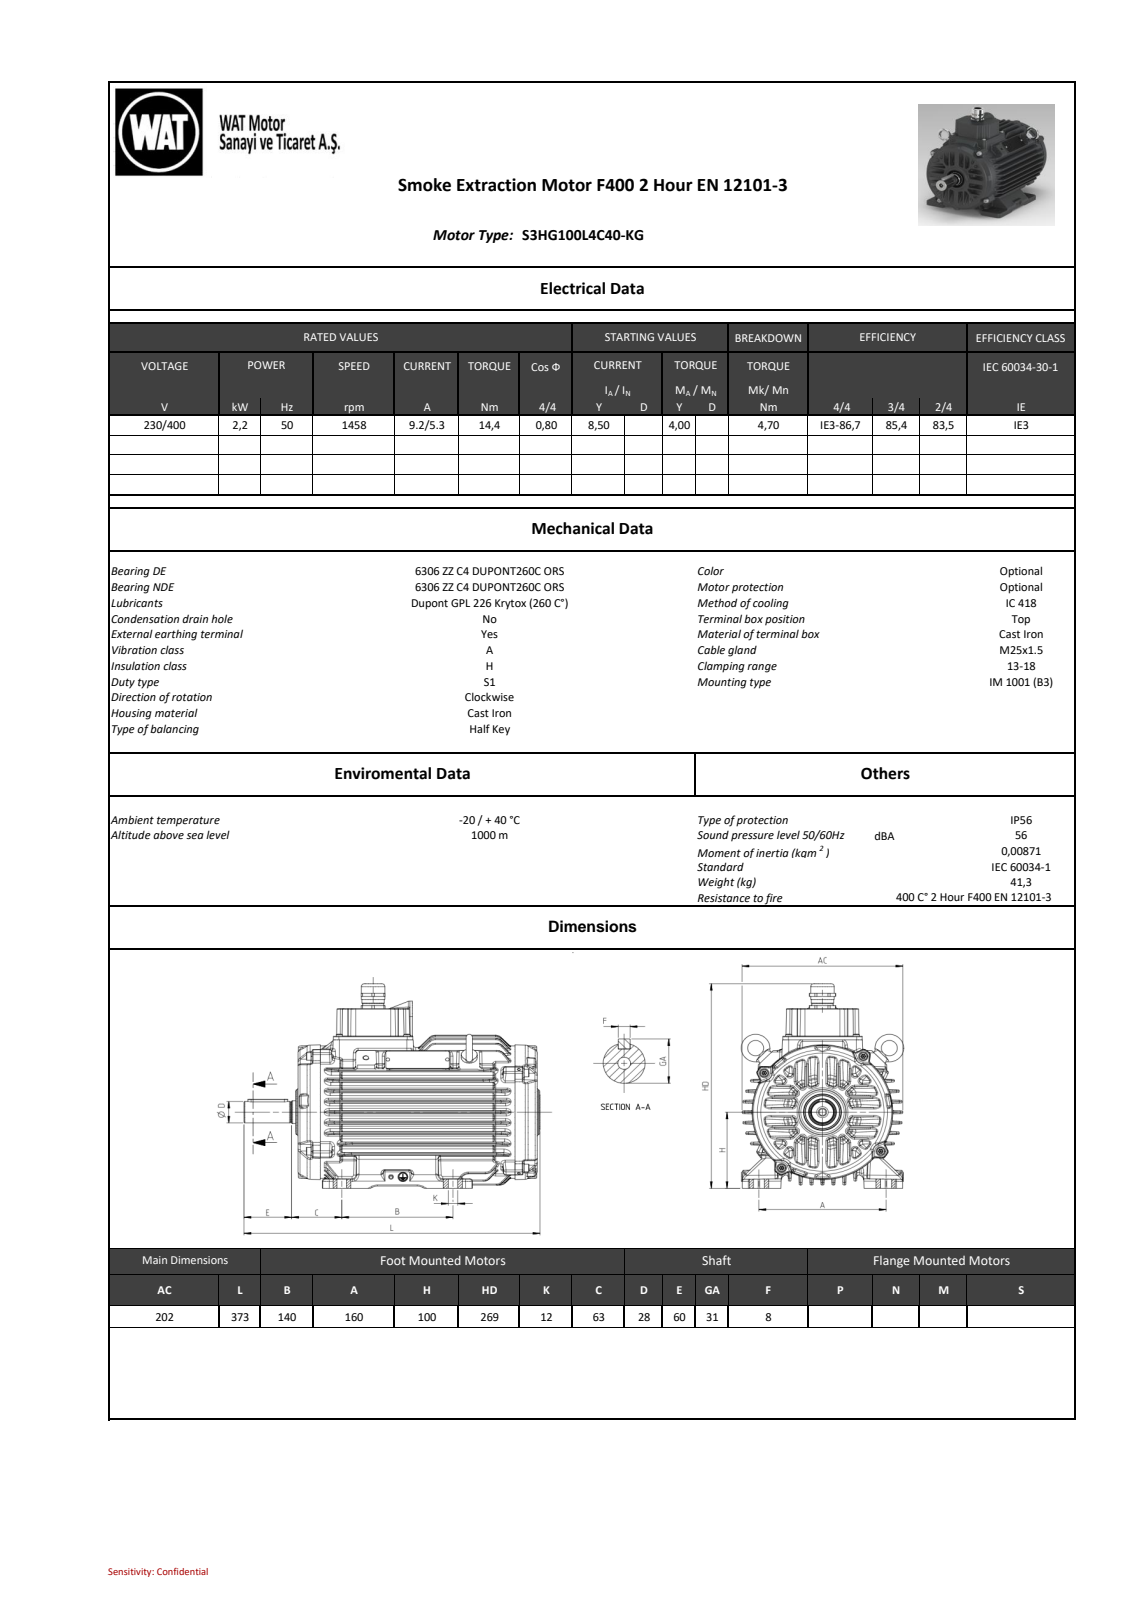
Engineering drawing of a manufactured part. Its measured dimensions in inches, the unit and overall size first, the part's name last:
Units: inches
Overall size (bounding box): 14.665 × 10.579 × 8.043
Round holes (diameter × count): ⌀0.197 ×8, ⌀0.13 ×4, ⌀0.098 ×2, ⌀0.268 ×2, ⌀0.165 ×1, ⌀0.413 ×1, ⌀0.709 ×1, ⌀1.299 ×1, ⌀1.693 ×1
Round bosses / shafts (diameter × count): ⌀0.465 ×8, ⌀0.394 ×8, ⌀0.315 ×4, ⌀0.787 ×2, ⌀6.85 ×1, ⌀1.85 ×1, ⌀1.181 ×1, ⌀1.165 ×1
Partial cylindrical surfaces — rounded edges, fillets, slot ends (radius × count): R0.118 ×420, R0.059 ×110, R0.079 ×81, R0.01 ×55, R0.071 ×48, R0.039 ×38, R0.197 ×20, R0.02 ×12
Main face-to-face distances: 0.532, 0.536, 1.068, 3.099, 2.031, 2.563, 1.607, 1.075, 0.539, 1.492
Hole centre spacings: 3.524, 4.983, 1.223, 4.043, 5.772, 6.94, 7.047, 1.083
Bodies: 0 solids, 5135 faces (704 planar, 1214 cylindrical, 3217 other)
Part name (STEP PRODUCT): 26032C0836B7xhuc
STEP written by: SIEMENS PLM Software NX 11.0 (AUTOMOTIVE_DESIGN)
